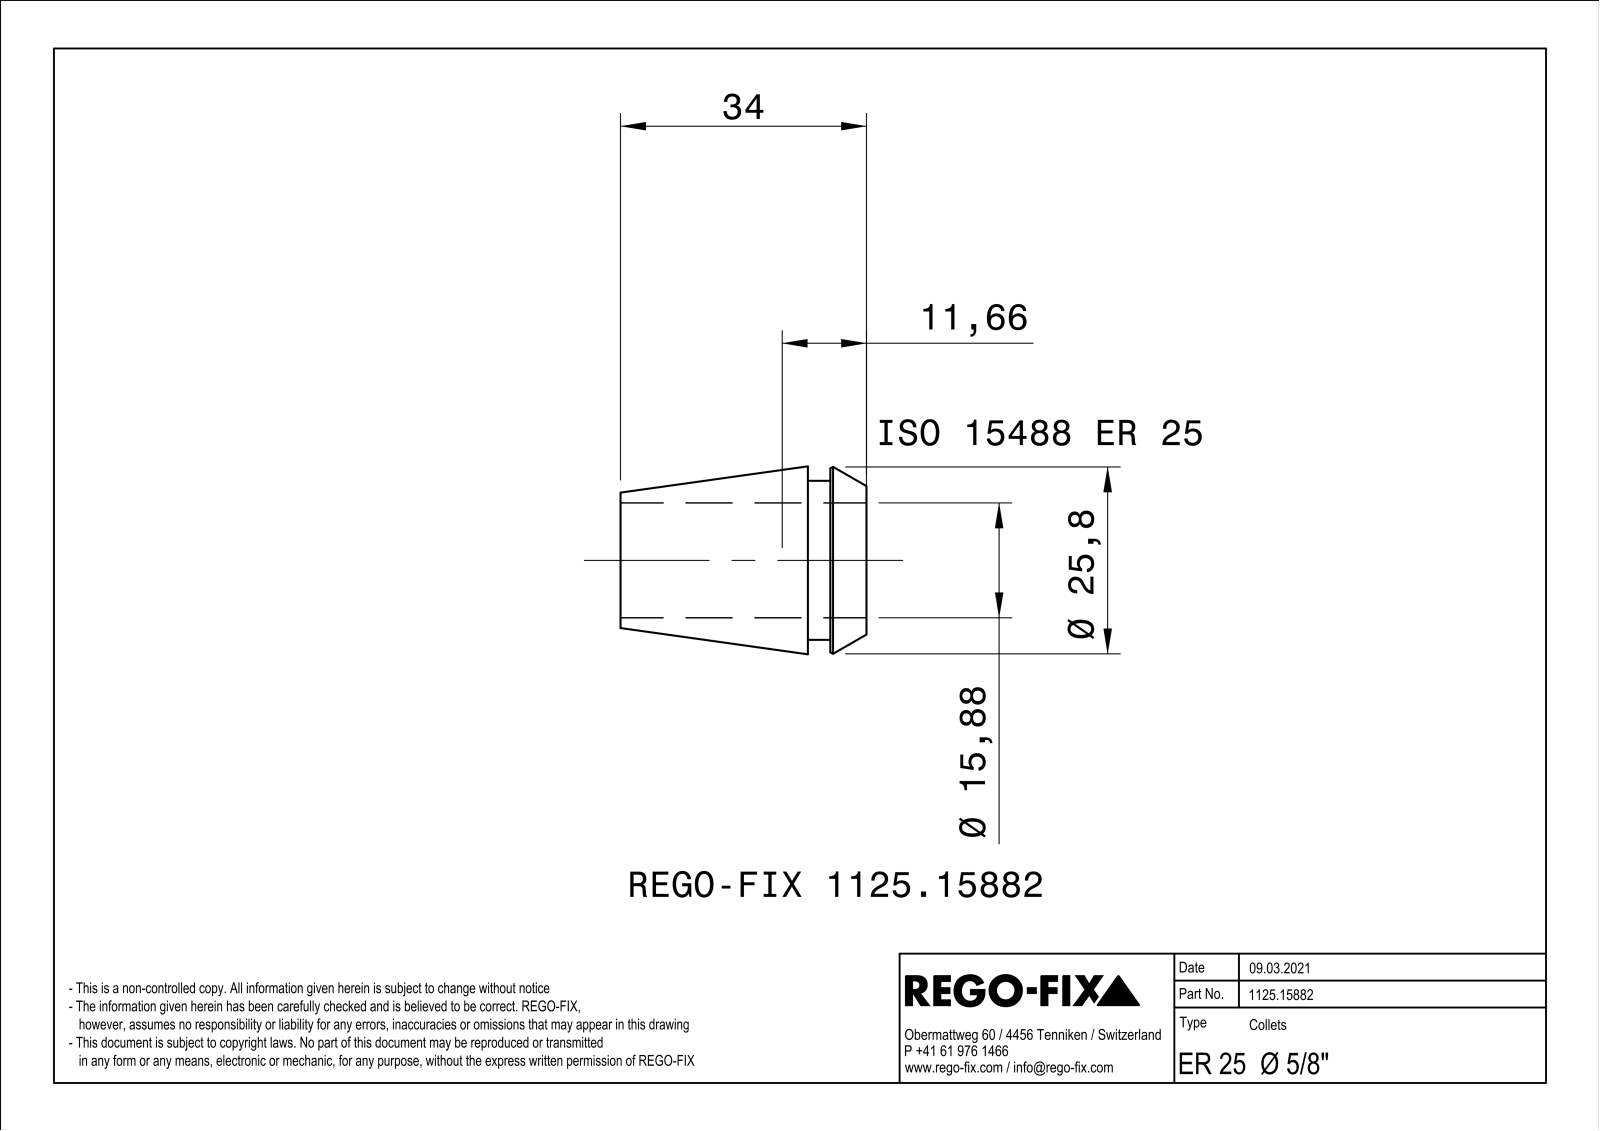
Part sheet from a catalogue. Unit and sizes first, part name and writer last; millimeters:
Units: millimetres
Overall size (bounding box): 34 × 25.99 × 25.99
Round holes (diameter × count): ⌀15.88 ×1
Round bosses / shafts (diameter × count): ⌀22 ×1
Partial cylindrical surfaces — rounded edges, fillets, slot ends (radius × count): R0.4 ×8
Main face-to-face distances: 0.8, 3.1, 5, 8.1, 34, 29, 25.9
Volume: 5 592 mm³ · Surface area: 7 017 mm²
Bodies: 1 solid, 177 faces (72 planar, 25 cylindrical, 80 other)
Part name (STEP PRODUCT): NOCUT
STEP written by: SIEMENS PLM Software Solid Edge ST10 (AUTOMOTIVE_DESIGN)
